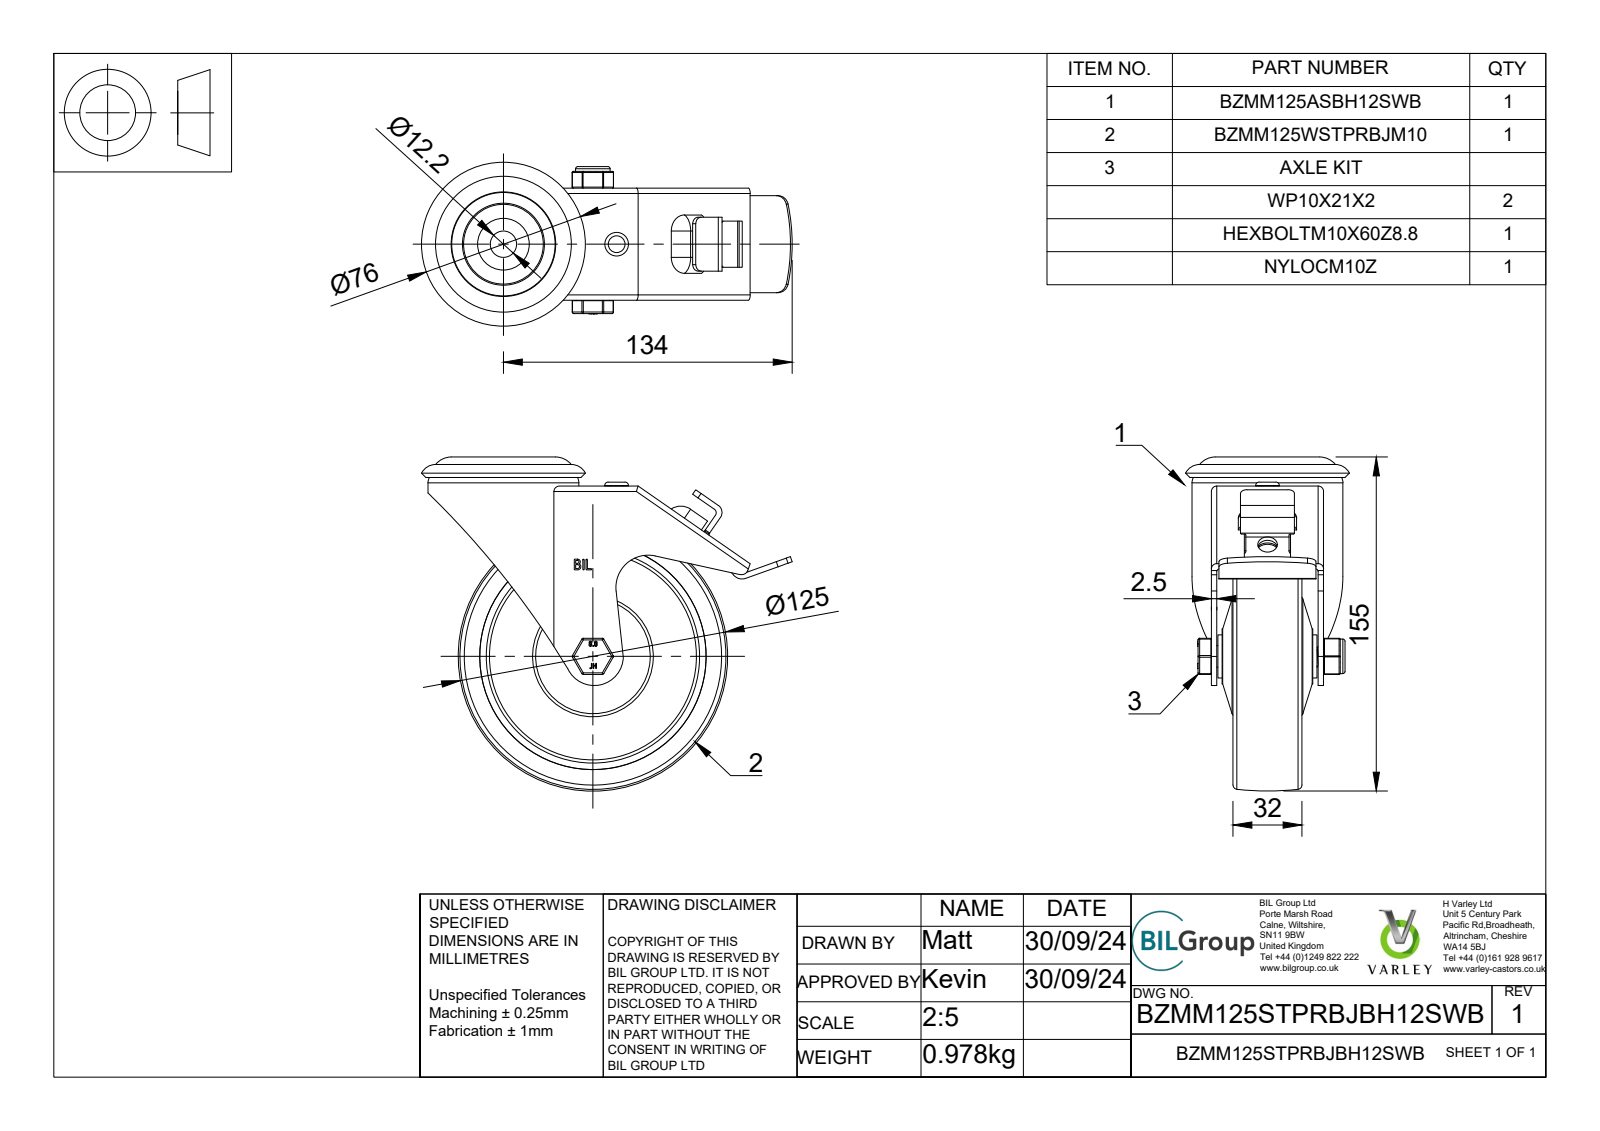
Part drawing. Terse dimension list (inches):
name: BZMM125STPRBJBH12SWB v3; BZMM125ASBH12SWB - 47 v1; ZINC PLATED, PRESSED STEEL HEAD; ZINC PLATED, PRESSED STEEL FORKS (+8 more)
written by: Autodesk Translation Framework v13.20.0.188 (AUTOMOTIVE_DESIGN)
unit: in
bodies: 28 solids, 1017 faces (444 planar, 278 cylindrical, 295 other)
size: 6.772 × 6.102 × 2.992
volume: 18.54 in³; area: 277.6 in²
holes: 2× ⌀0.236, 1× ⌀0.354, 1× ⌀0.394, 1× ⌀0.402, 1× ⌀0.409, 1× ⌀0.423, 1× ⌀0.472, 1× ⌀0.48, 1× ⌀0.886, 1× ⌀1.181, 1× ⌀1.22, 1× ⌀1.26
bosses: 1× ⌀2.756, 1× ⌀2.205, 1× ⌀1.949, 1× ⌀1.752, 1× ⌀1.535, 1× ⌀1.496, 1× ⌀1.358, 1× ⌀1.201
rounds: 60× R0.03, 32× R0.02, 6× R0.049, 6× R0.118, 6× R0.157, 5× R0.098, 3× R0.079, 3× R0.197
face distances: 0.098, 1.014, 1.112, 0.295, 0.837, 0.541, 1.654, 0.935, 0.394, 1.949
hole spacings: 2.067
